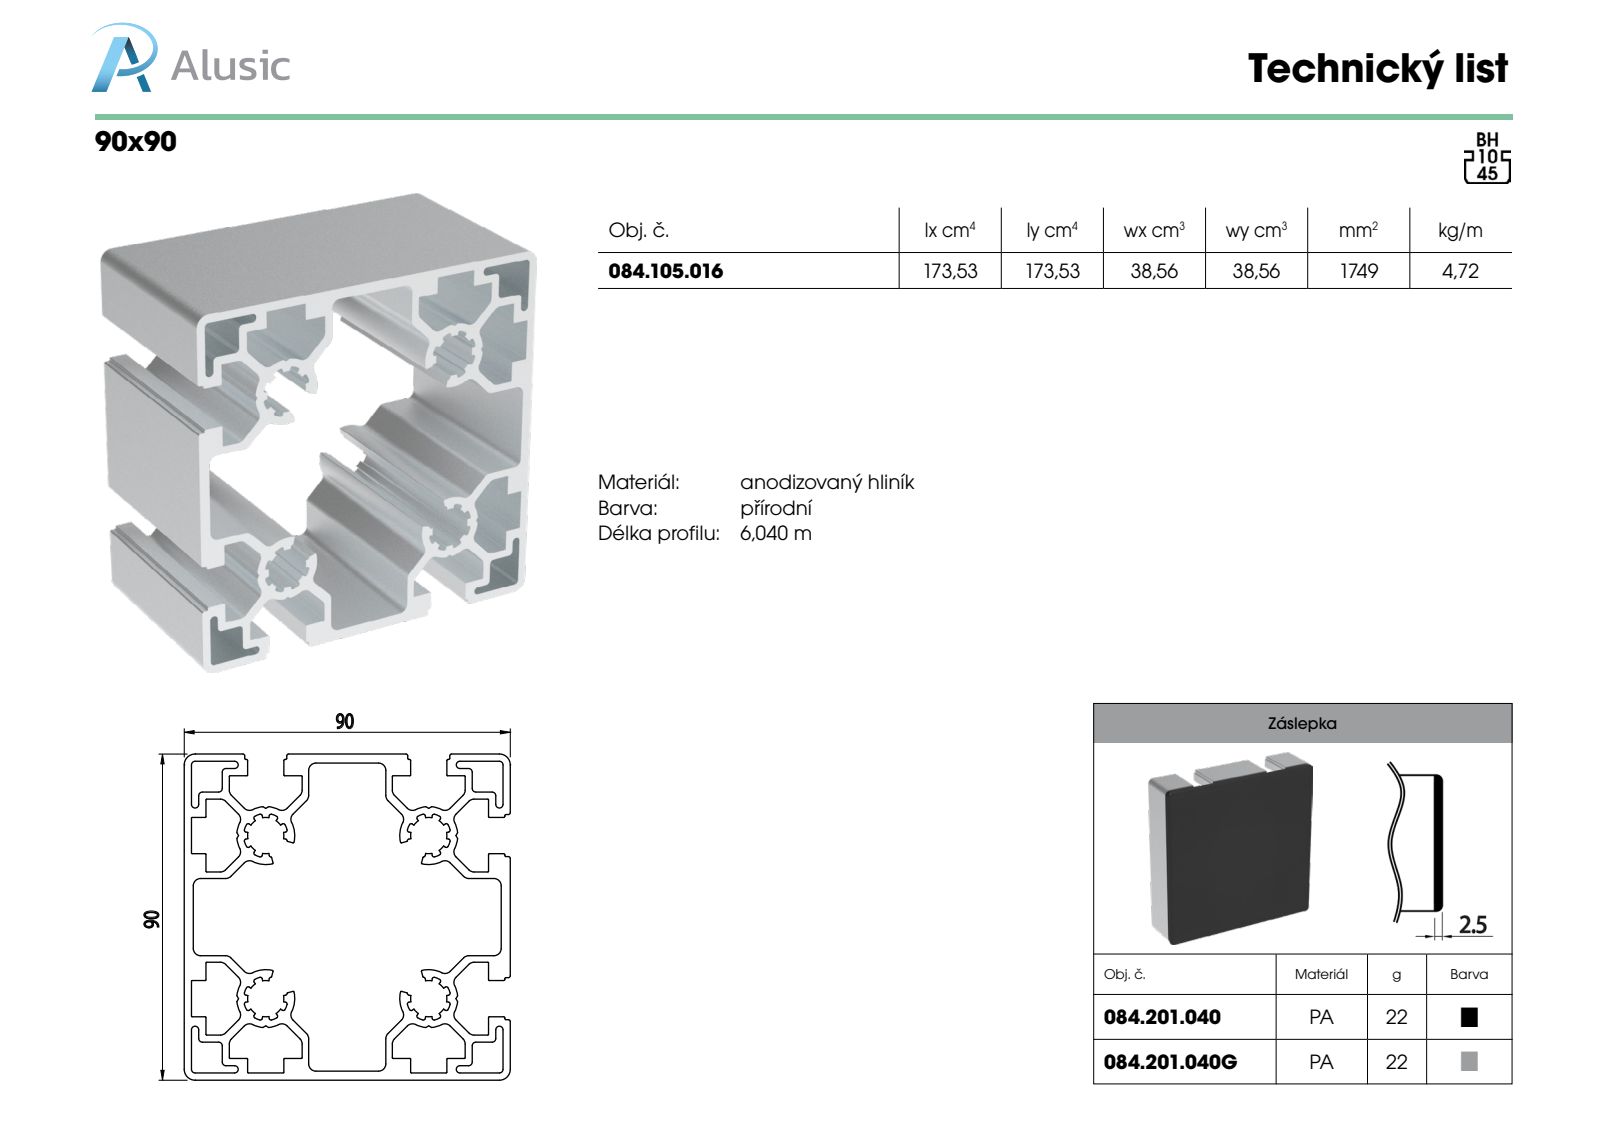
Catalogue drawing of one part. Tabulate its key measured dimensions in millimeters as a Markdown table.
| quantity | value |
| --- | --- |
| part name | 084.105.016 |
| STEP written by | SolidWorks 2018 (AUTOMOTIVE_DESIGN) |
| units | millimeters |
| bodies | 1 solid, 542 faces (218 planar, 324 cylindrical, 0 other) |
| overall size | 100 × 90 × 90 |
| volume | 174 995 mm³ |
| surface area | 145 797 mm² |
| partial cylindrical surfaces (radius × count) | 0.5 × 64, 0.2 × 56, 2 × 56, 1 × 24, 0.3 × 16, 3 × 4, 5 × 4, 6.1 × 4 |
| main face-to-face distances | 2, 88, 90, 6, 4, 84, 82, 2.5, 87.5, 0.5 |
